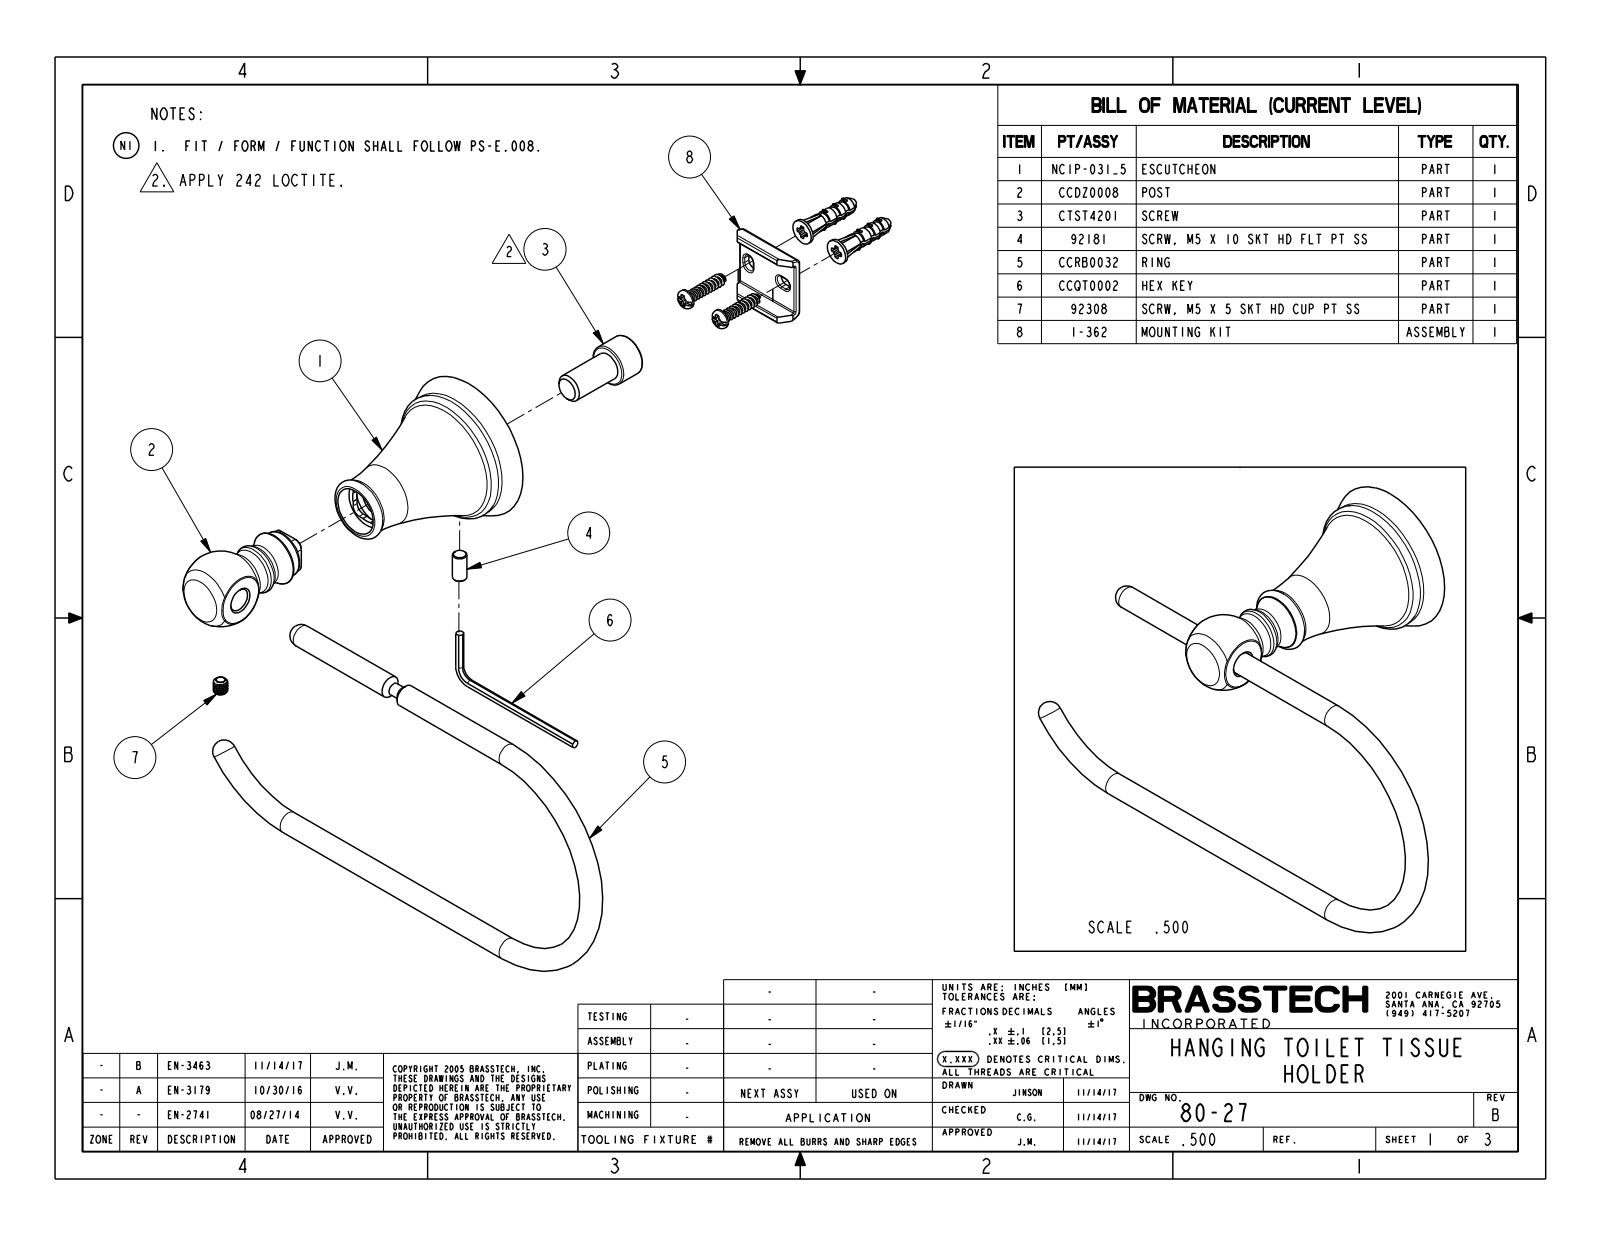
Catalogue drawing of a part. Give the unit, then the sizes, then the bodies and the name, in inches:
Units: inches
Overall size (bounding box): 7.442 × 4.475 × 3.72
Round holes (diameter × count): ⌀0.165 ×2, ⌀0.236 ×2, ⌀0.213 ×1, ⌀0.327 ×1, ⌀0.339 ×1, ⌀0.394 ×1, ⌀0.417 ×1, ⌀0.669 ×1, ⌀0.685 ×1, ⌀0.945 ×1, ⌀1.68 ×1, ⌀1.93 ×1
Round bosses / shafts (diameter × count): ⌀0.315 ×2, ⌀0.197 ×2, ⌀0.585 ×1, ⌀0.177 ×1
Partial cylindrical surfaces — rounded edges, fillets, slot ends (radius × count): R0.02 ×22, R0.118 ×8, R0.079 ×6, R0.089 ×4, R0.272 ×1
Main face-to-face distances: 0.098, 0.7, 0.602, 0.09, 0.61, 0.531, 0.079, 1.669, 1.235, 1.145
Hole centre spacings: 3.07
Volume: 3.23 in³ · Surface area: 48.76 in²
Bodies: 7 solids, 302 faces (92 planar, 94 cylindrical, 116 other)
Part name (STEP PRODUCT): NCIP-031_5; CCDZ0008; CTST4201; CCKT0030 (+4 more)
STEP written by: PRO/ENGINEER BY PARAMETRIC TECHNOLOGY CORPORATION, 2013150 (CONFIG_CONTROL_DESIGN)
